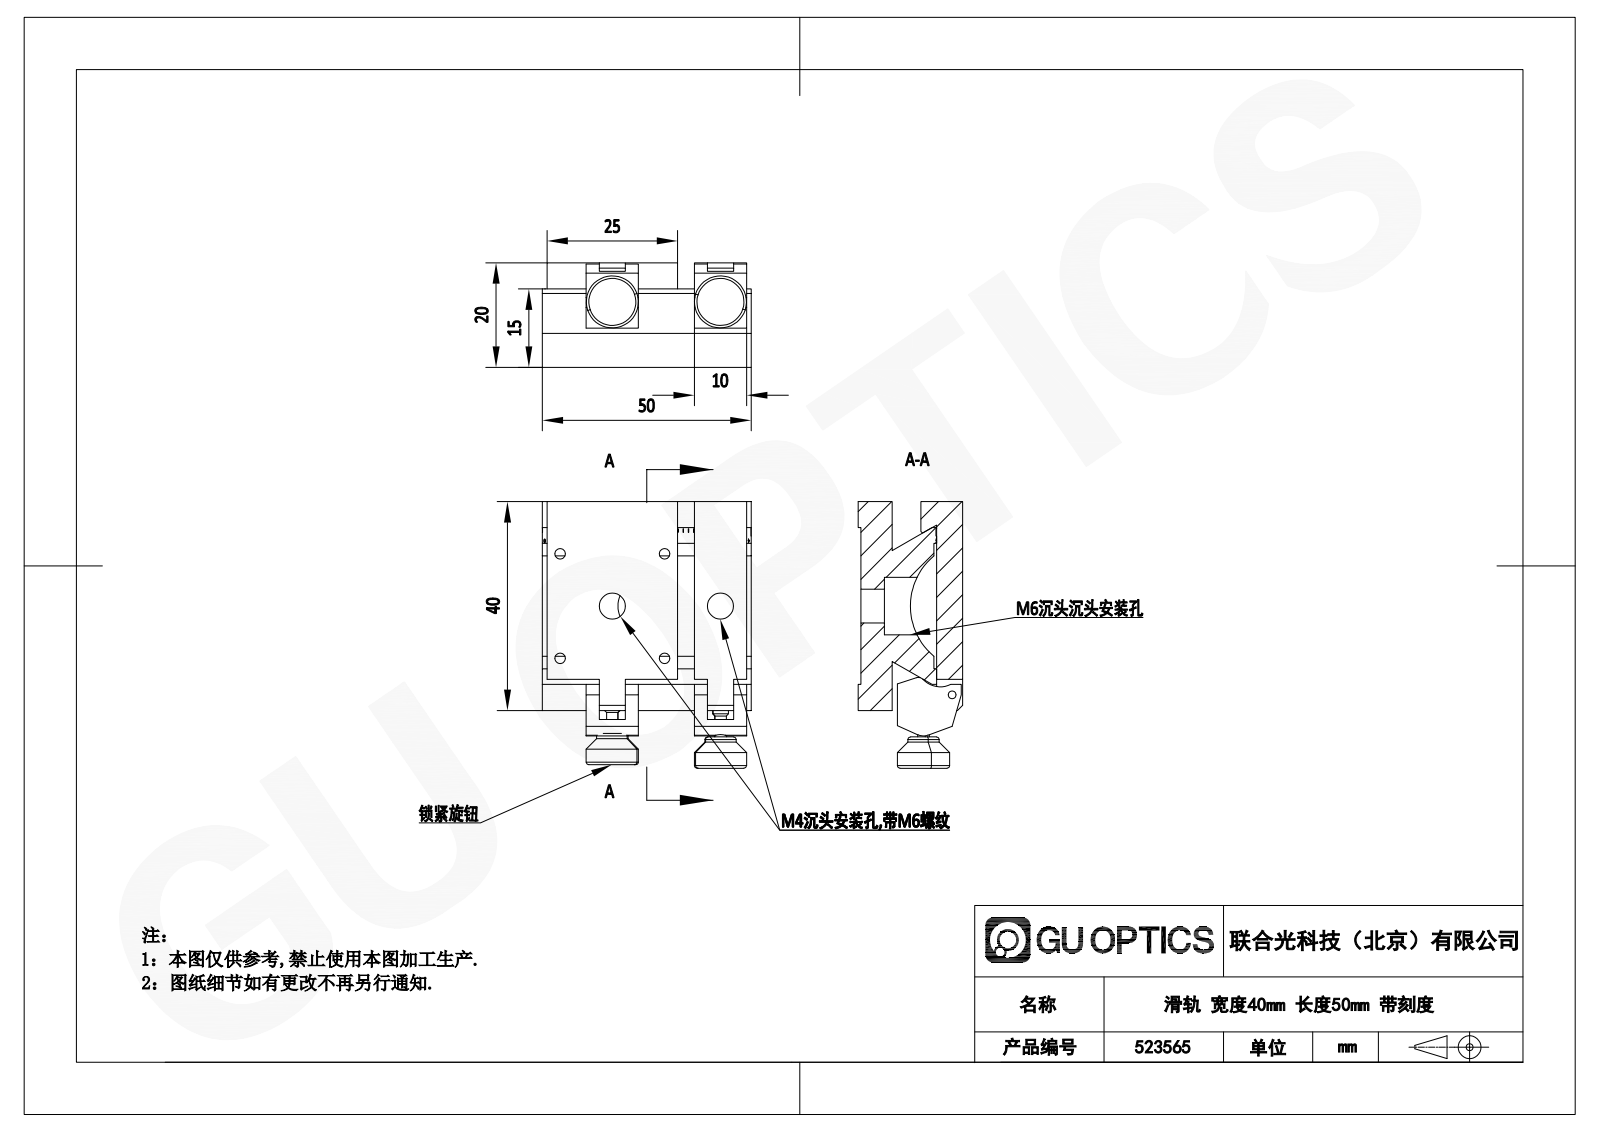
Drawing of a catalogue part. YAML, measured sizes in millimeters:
part_name: "523565"
step_written_by: "SolidWorks 2020 (CONFIG_CONTROL_DESIGN)"
units: millimeters
bodies: {solids: 8, faces: 511, planar: 361, cylindrical: 75, other: 75}
overall_size: [51.03, 40, 20]
volume: 23797
surface_area: 12772
round_holes:
  - {diameter: 2.05, count: 4}
  - {diameter: 2.5, count: 2}
  - {diameter: 3.2, count: 2}
  - {diameter: 5, count: 2}
  - {diameter: 8, count: 2}
  - {diameter: 1.5, count: 1}
  - {diameter: 2, count: 1}
  - {diameter: 6.5, count: 1}
  - {diameter: 11, count: 1}
round_bosses_or_shafts:
  - {diameter: 10, count: 2}
  - {diameter: 6, count: 2}
  - {diameter: 3, count: 2}
  - {diameter: 2.2, count: 2}
partial_cylinders:
  - {radius: 1.25, count: 1}
  - {radius: 2.5, count: 1}
  - {radius: 4.5, count: 1}
  - {radius: 12.5, count: 1}
face_to_face_distances: [5, 14.5, 19.5, 6, 7.5, 2.5, 8.5, 13.5, 40, 15]
hole_center_spacings: [14.14, 20, 10.57, 14.66, 19.37, 20.72, 28.28, 32.31]
